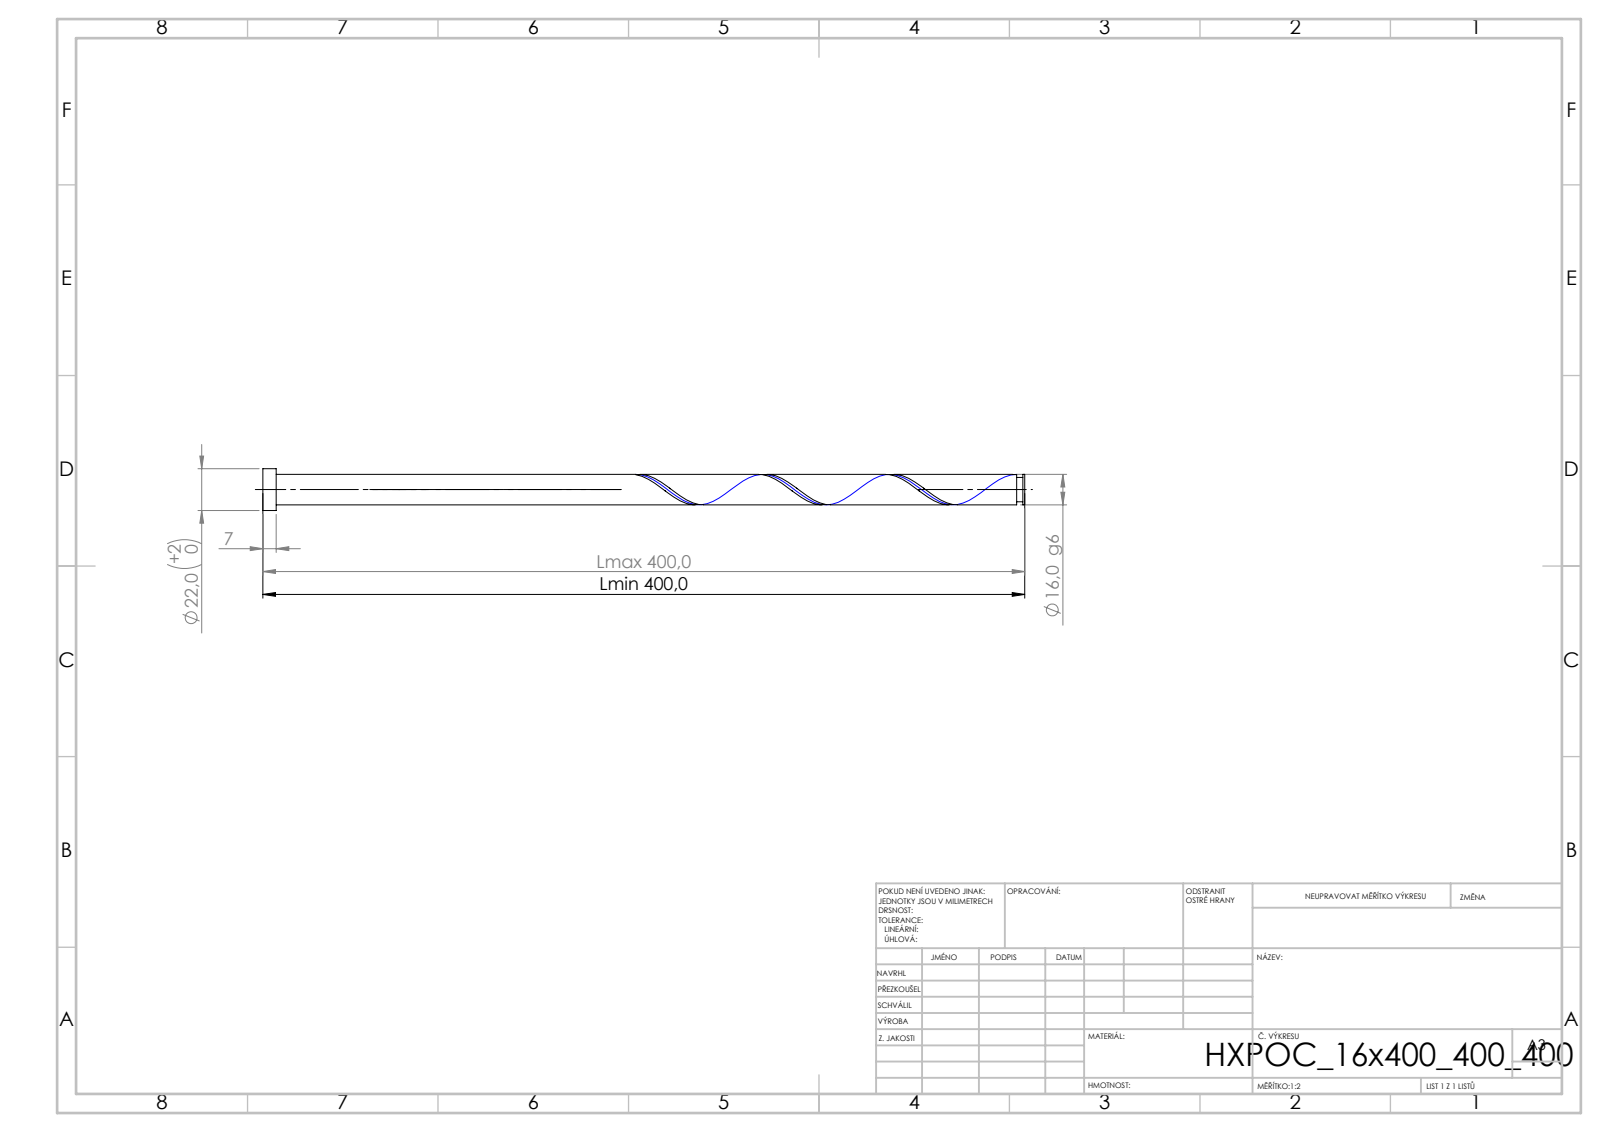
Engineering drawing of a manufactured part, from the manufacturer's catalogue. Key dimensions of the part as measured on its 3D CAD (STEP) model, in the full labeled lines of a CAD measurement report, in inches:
STEP written by: SolidWorks 2019 (CONFIG_CONTROL_DESIGN)
Units: inches
Bodies: 1 solid, 21 faces (6 planar, 14 cylindrical, 1 other)
Overall size (bounding box): 15.748 × 0.866 × 0.866
Volume: 4.923 in³ · Surface area: 33.36 in²
Round bosses / shafts (diameter × count): ⌀0.866 ×1, ⌀0.63 ×1, ⌀0.504 ×1
Main face-to-face distances: 15.748, 0.276, 15.472, 15.707, 15.432, 0.041, 15.581, 15.306, 0.126, 0.167
